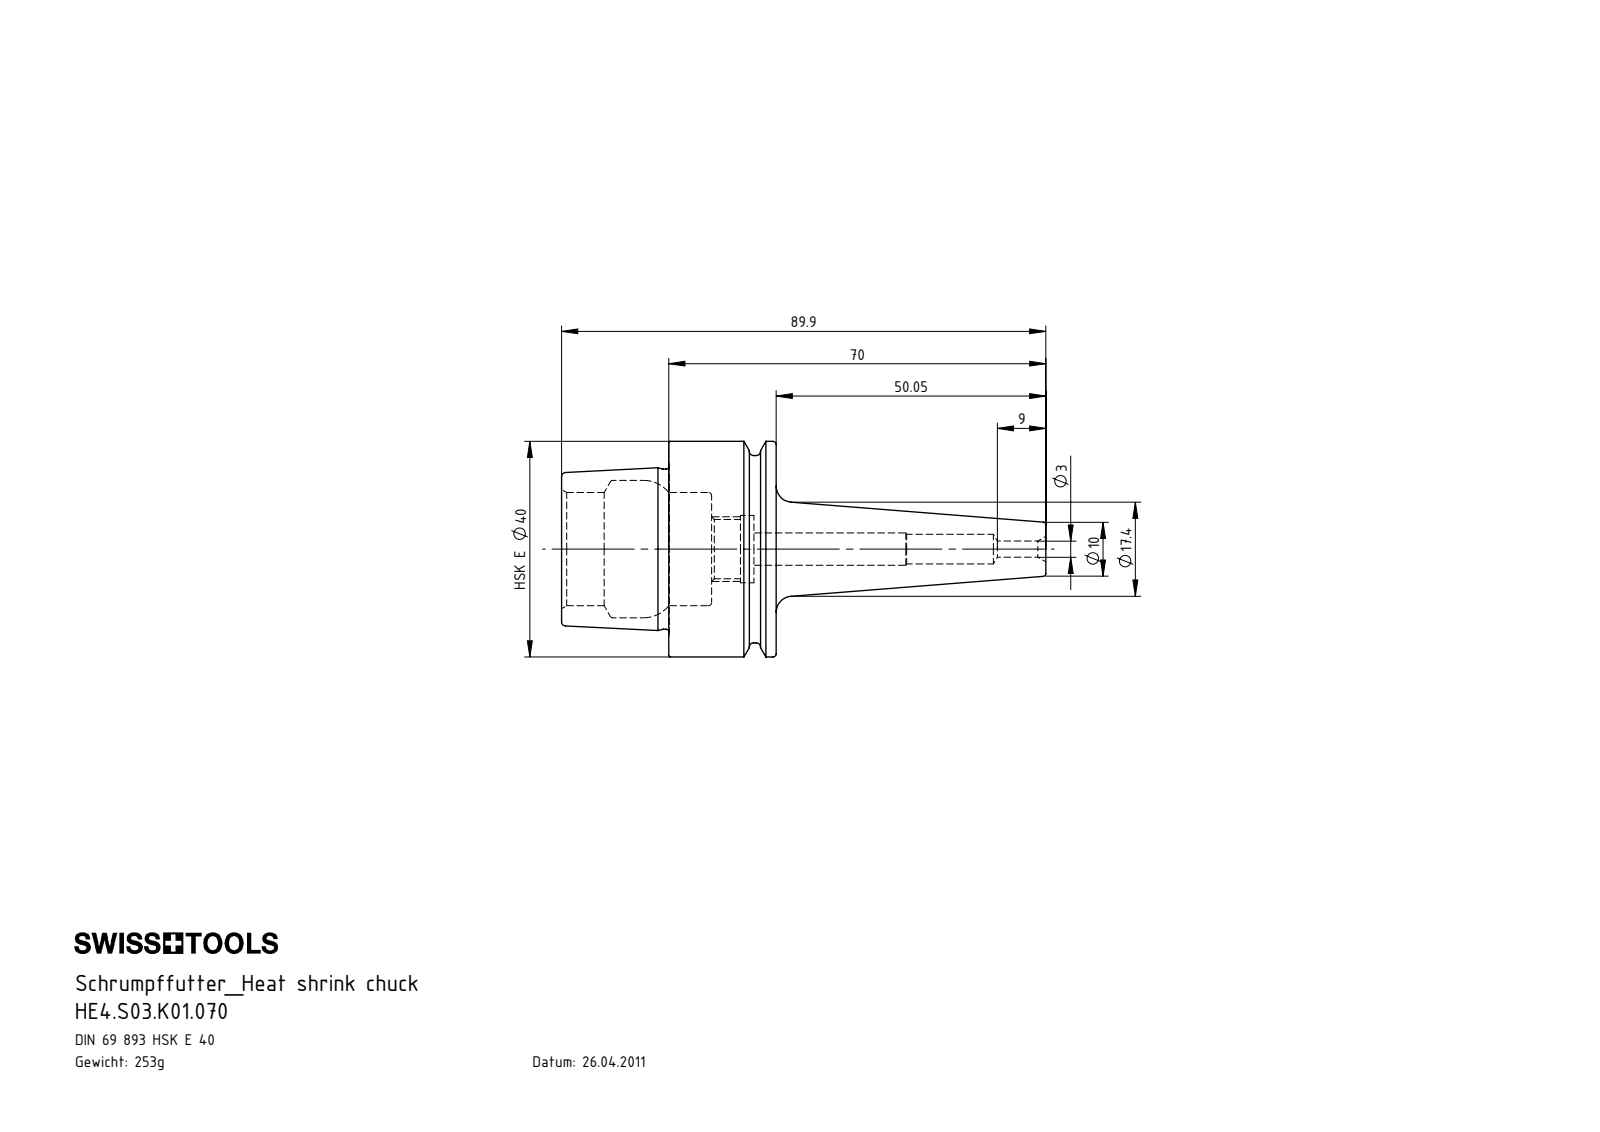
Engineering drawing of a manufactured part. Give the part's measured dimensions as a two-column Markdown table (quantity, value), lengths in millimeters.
| quantity | value |
| --- | --- |
| part name | HE4.S03.K01.070 |
| STEP written by | SolidWorks 2017 (CONFIG_CONTROL_DESIGN) |
| units | millimeters |
| bodies | 1 solid, 81 faces (9 planar, 24 cylindrical, 48 other) |
| overall size | 89.9 × 40 × 40 |
| volume | 32 278 mm³ |
| surface area | 12 281 mm² |
| round holes (diameter × count) | 3 × 1, 5.5 × 1, 6 × 1, 11 × 1, 12.5 × 1, 21 × 1, 25.5 × 1 |
| round bosses / shafts (diameter × count) | 40 × 1, 34.75 × 1, 29.71 × 1 |
| main face-to-face distances | 19.95, 7.95, 12, 19.9, 27.85, 39.85, 35.7, 15.8, 7.85, 4.15 |
